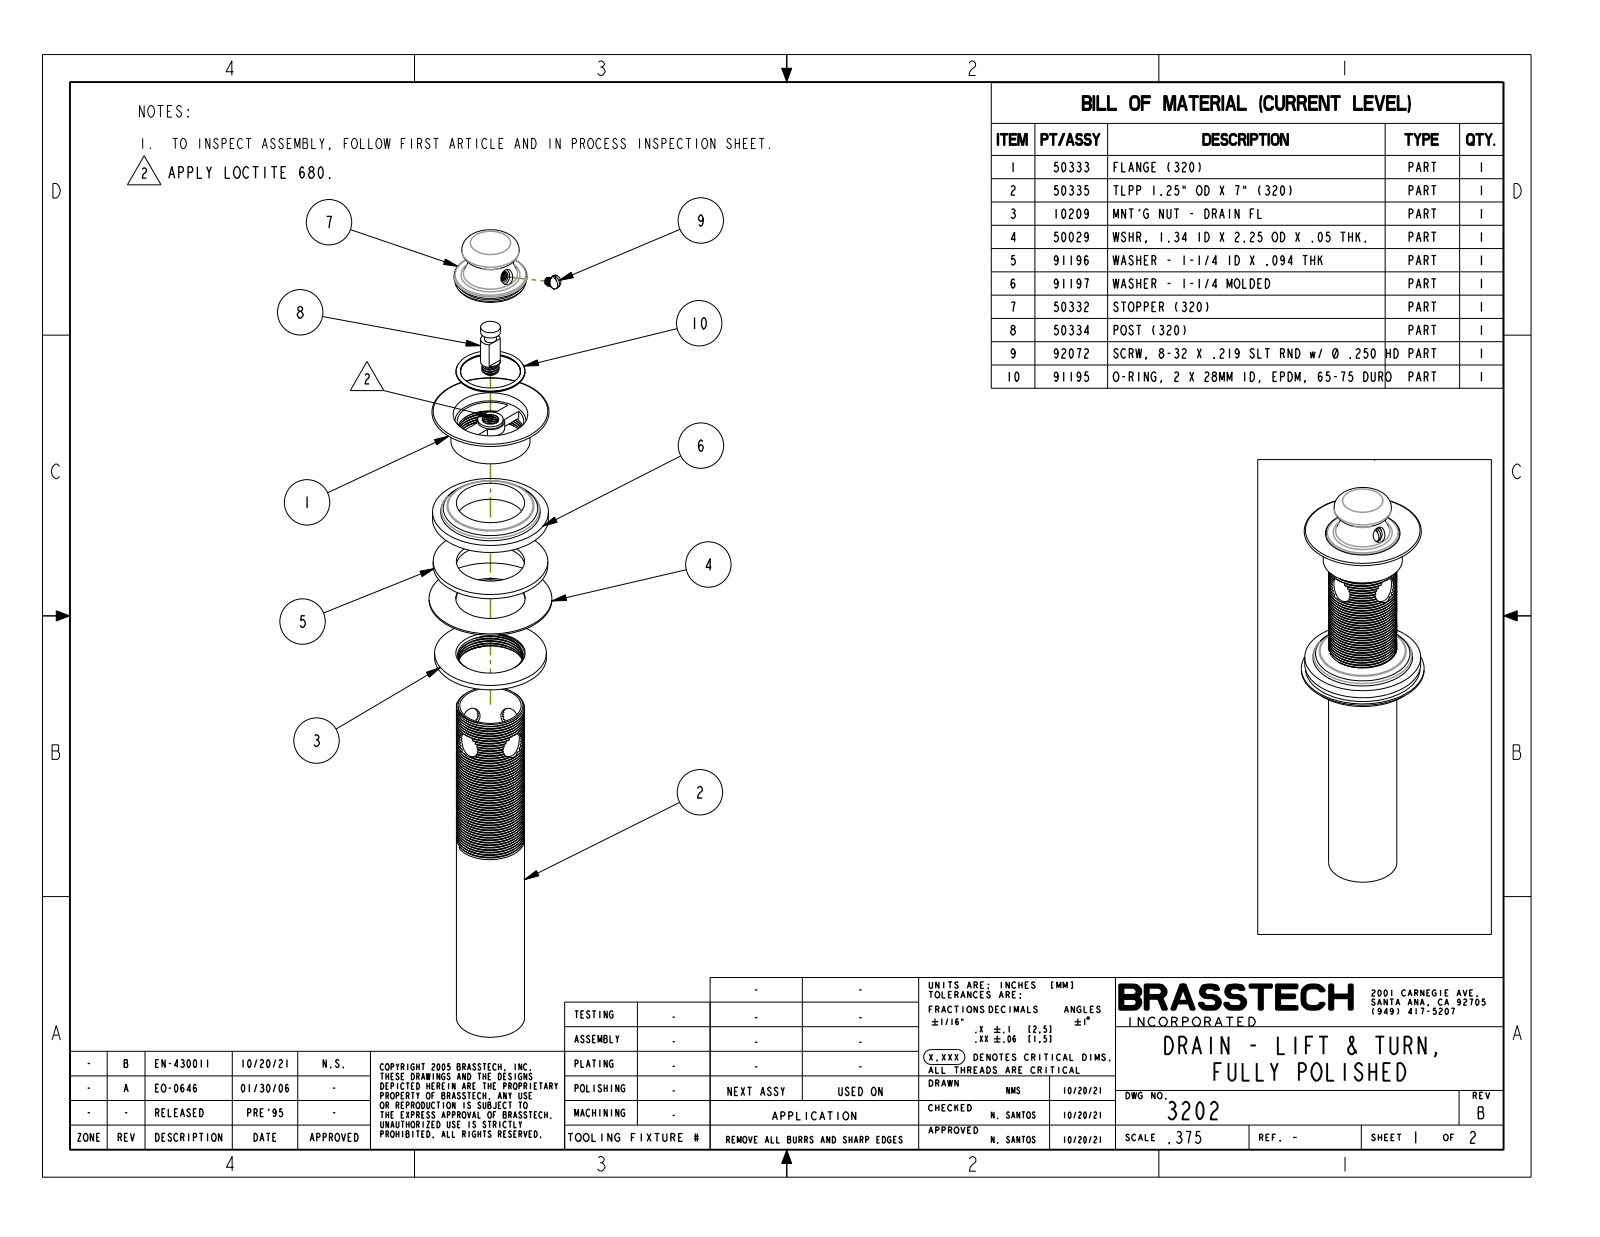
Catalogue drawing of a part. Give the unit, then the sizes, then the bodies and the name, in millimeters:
Units: millimetres
Overall size (bounding box): 206.3 × 57.2 × 57.2
Round holes (diameter × count): ⌀12.1 ×2, ⌀3.4 ×1, ⌀6.4 ×1, ⌀7.1 ×1, ⌀30.2 ×1, ⌀30.5 ×1
Round bosses / shafts (diameter × count): ⌀57.2 ×1, ⌀54 ×1, ⌀53.3 ×1, ⌀52.1 ×1, ⌀36.8 ×1, ⌀34.8 ×1, ⌀33.9 ×1, ⌀31.8 ×1
Partial cylindrical surfaces — rounded edges, fillets, slot ends (radius × count): R3.3 ×6, R6.4 ×1
Main face-to-face distances: 5.1, 10.2, 7.6, 8.4, 0.8, 22.9, 15.2, 14.5, 15.1, 7.5
Volume: 131 400 mm³ · Surface area: 95 550 mm²
Bodies: 2 solids, 620 faces (51 planar, 336 cylindrical, 233 other)
Part name (STEP PRODUCT): 3202
STEP written by: CREO PARAMETRIC BY PTC INC, 2018500 (CONFIG_CONTROL_DESIGN)
